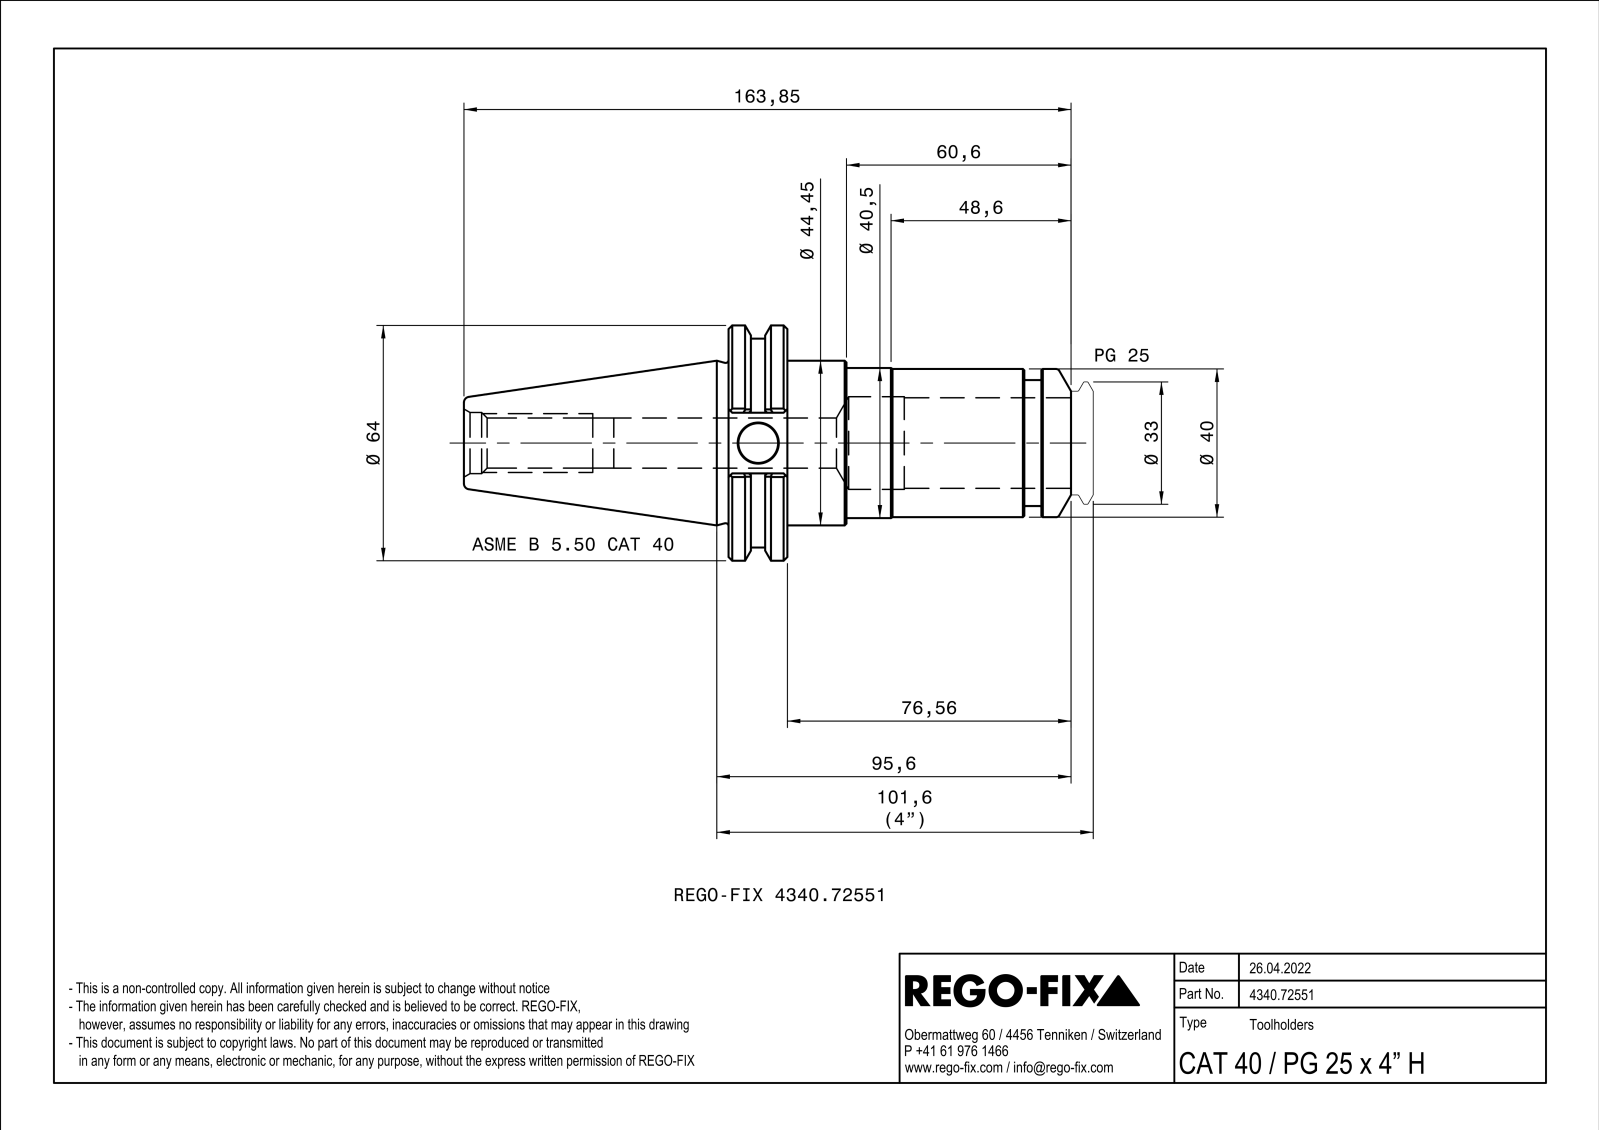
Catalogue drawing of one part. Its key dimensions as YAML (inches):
part_name: "NOCUT"
step_written_by: "SIEMENS PLM Software Solid Edge ST10 (AUTOMOTIVE_DESIGN)"
units: inches
bodies: {solids: 1, faces: 106, planar: 34, cylindrical: 22, other: 50}
overall_size: [6.451, 2.5, 2.393]
volume: 10.15
surface_area: 54.98
round_holes:
  - {diameter: 0.421, count: 1}
  - {diameter: 0.533, count: 1}
  - {diameter: 0.65, count: 1}
  - {diameter: 0.984, count: 1}
round_bosses_or_shafts:
  - {diameter: 2.5, count: 1}
  - {diameter: 2.219, count: 1}
  - {diameter: 1.75, count: 1}
  - {diameter: 1.594, count: 1}
  - {diameter: 1.575, count: 1}
  - {diameter: 1.339, count: 1}
partial_cylinders:
  - {radius: 0.02, count: 4}
face_to_face_distances: [0.625, 2.518, 3.143, 0.181, 2.699, 3.324, 1.863, 0.645, 2.071, 1.89]
